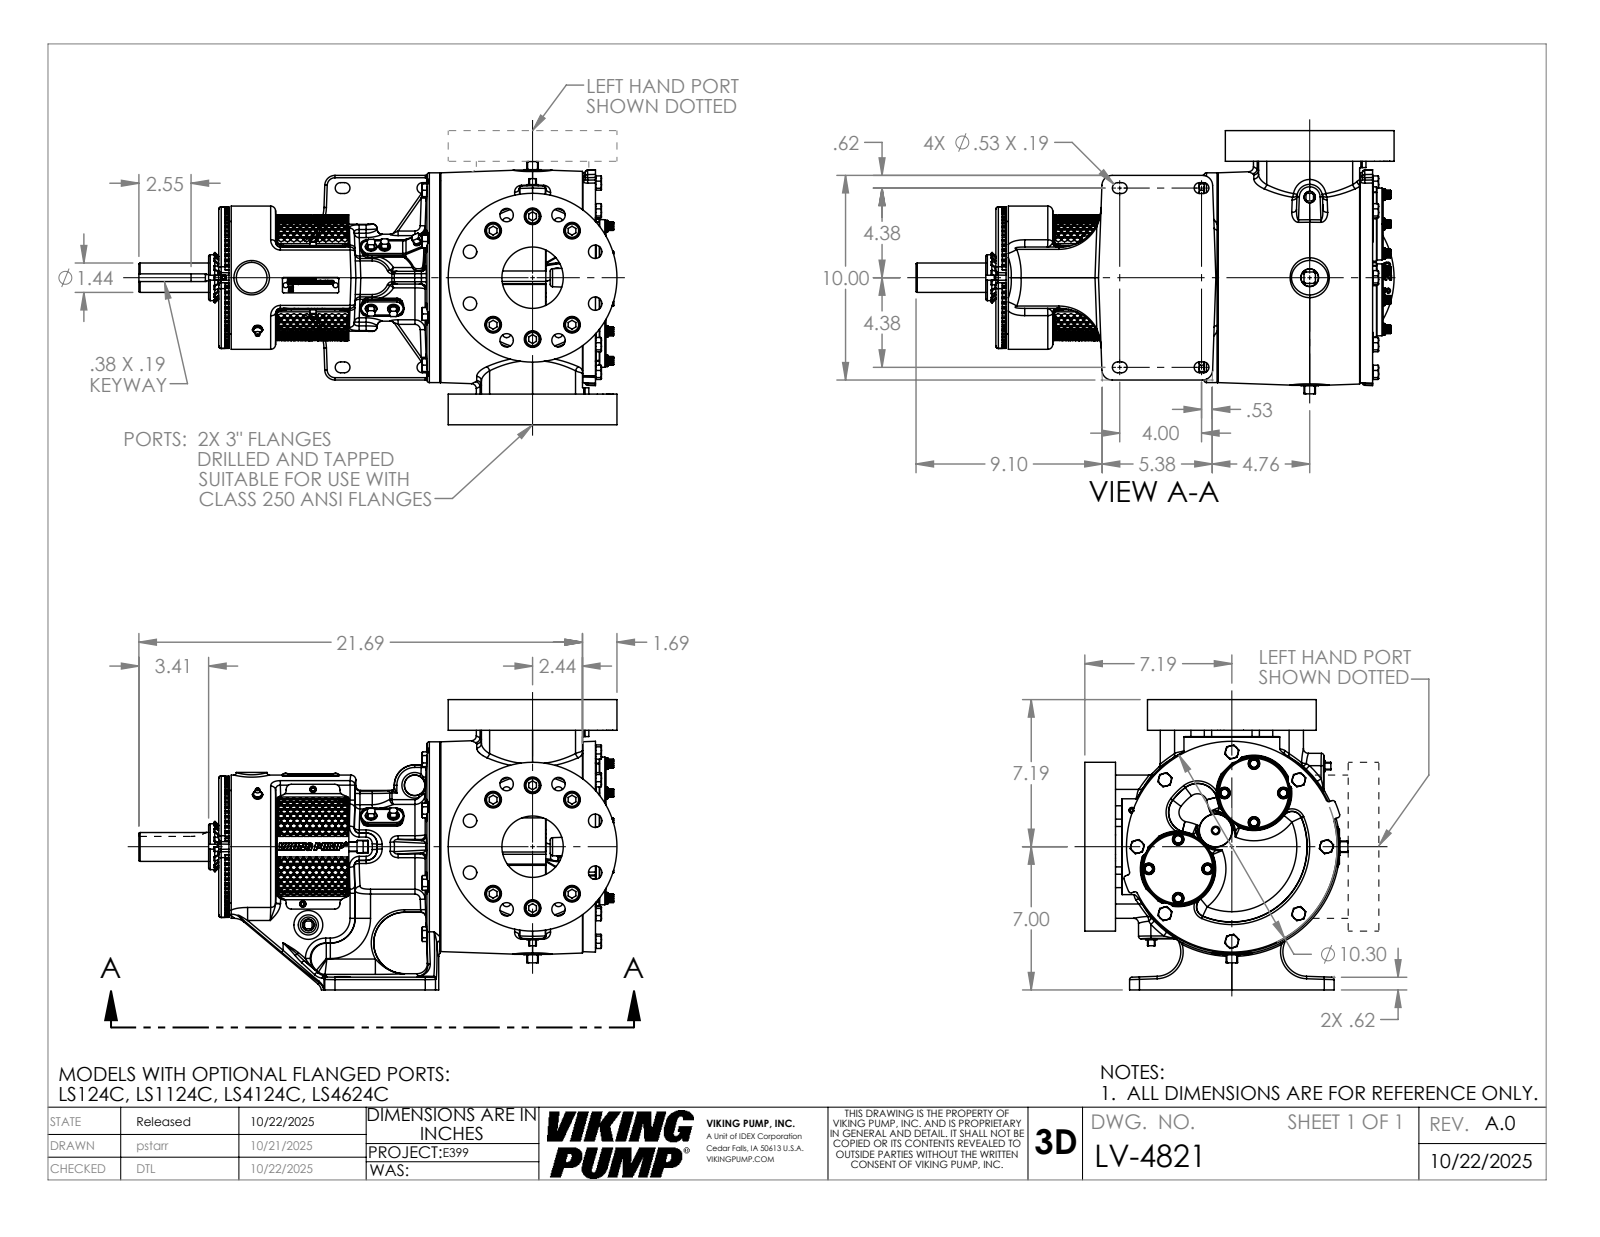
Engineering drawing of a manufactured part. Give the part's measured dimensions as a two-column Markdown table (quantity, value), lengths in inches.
| quantity | value |
| --- | --- |
| part name | LV-4821 |
| STEP written by | SolidWorks 2024 (AUTOMOTIVE_DESIGN) |
| units | inches |
| bodies | 1 solid, 4987 faces (1739 planar, 1054 cylindrical, 2194 other) |
| overall size | 23.372 × 14.187 × 12.863 |
| volume | 1 139 in³ |
| surface area | 1 503 in² |
| round holes (diameter × count) | 0.656 × 16, 0.812 × 12, 0.25 × 9, 1.094 × 8, 0.199 × 6, 0.159 × 3, 0.266 × 2, 0.313 × 2, 3 × 2, 0.453 × 1, 1.506 × 1, 1.578 × 1 |
| round bosses / shafts (diameter × count) | 0.75 × 12, 0.625 × 10, 0.563 × 8, 0.625 × 6, 0.312 × 3, 0.19 × 3, 8.25 × 2, 3.5 × 2 |
| partial cylindrical surfaces (radius × count) | 0.063 × 109, 0.12 × 78, 0.069 × 74, 0.24 × 48, 0.03 × 20, 1 × 16, 0.5 × 14, 0.25 × 12 |
| main face-to-face distances | 1.5, 14.187, 12.687, 0.5, 12.128, 3.541, 15.669, 16.184, 12.643, 0.515 |
| hole center spacings | 3, 3.313, 4.685, 6.12, 1.375, 1.009, 1.269, 1.531 |
